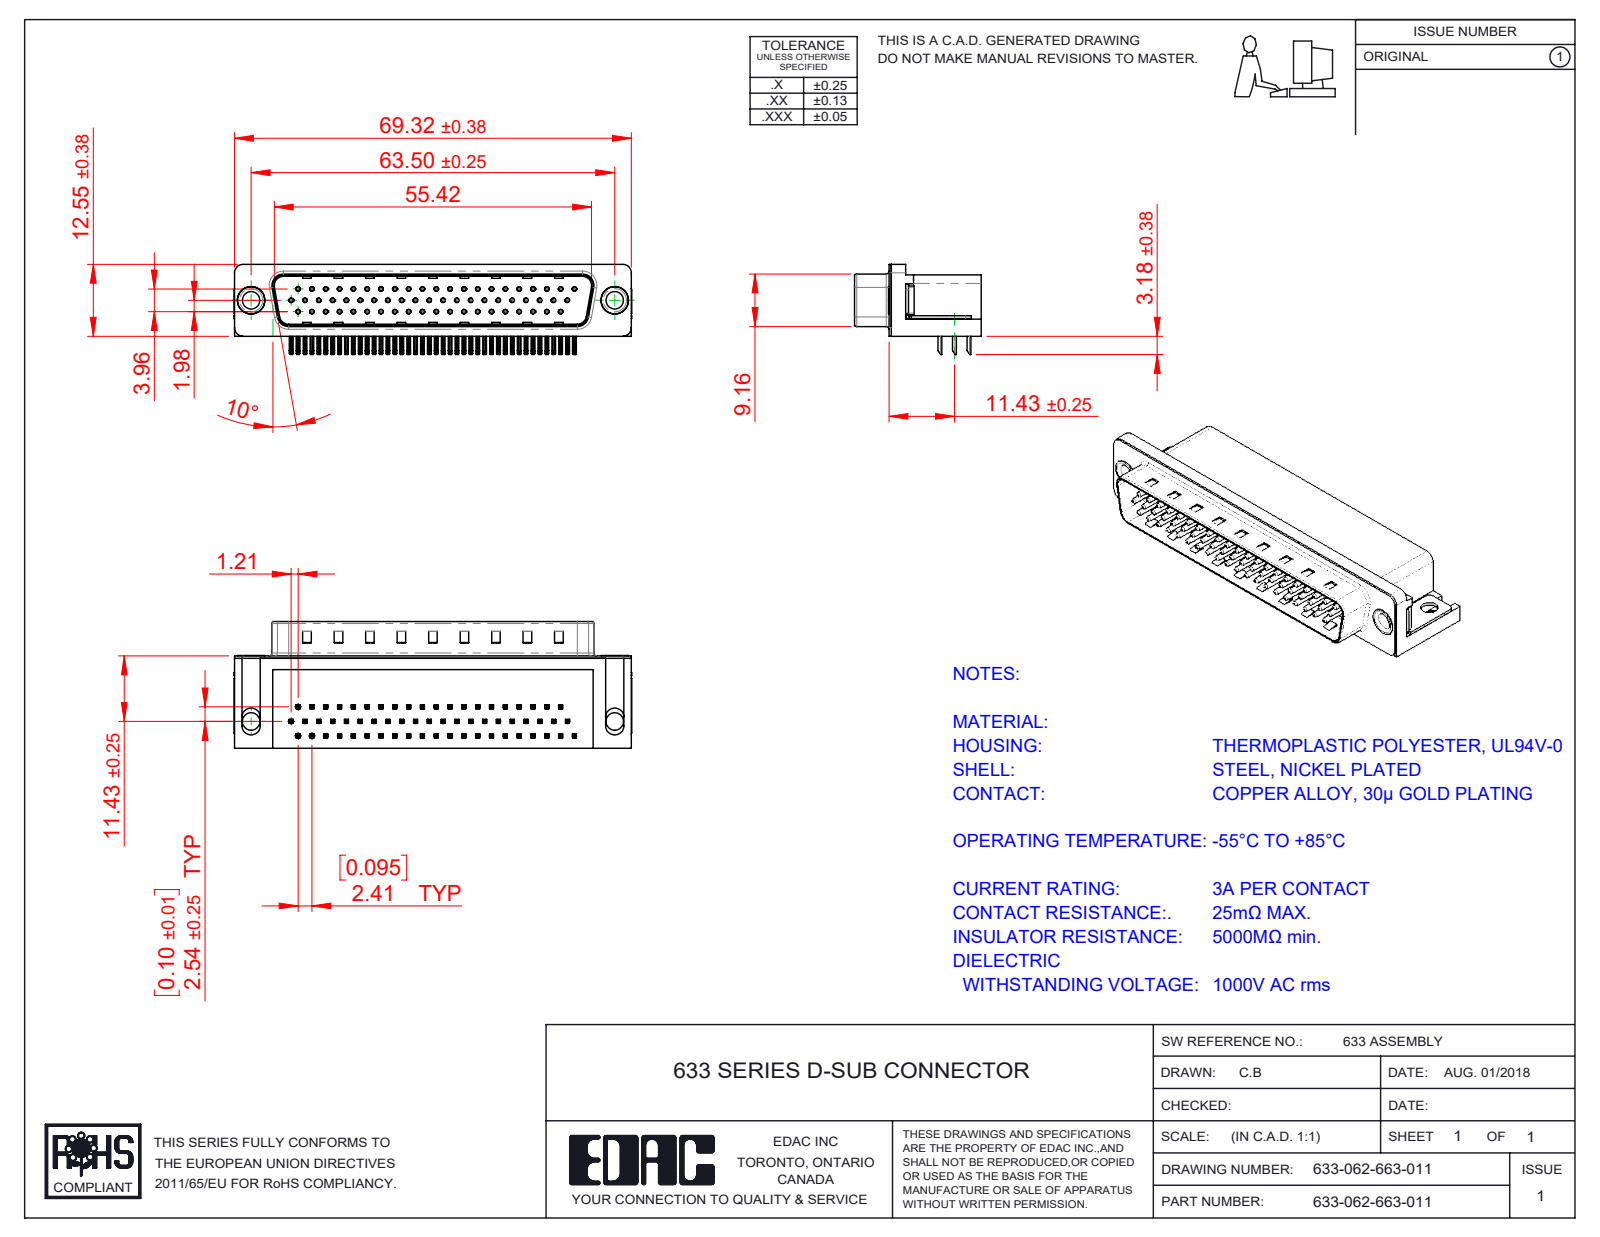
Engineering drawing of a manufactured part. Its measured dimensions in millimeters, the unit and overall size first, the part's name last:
Units: millimetres
Overall size (bounding box): 69.4 × 22.1 × 15.73
Round holes (diameter × count): ⌀0.35 ×62, ⌀0.8 ×62, ⌀3.05 ×4, ⌀4 ×2, ⌀4.8 ×2, ⌀5 ×2
Round bosses / shafts (diameter × count): ⌀0.75 ×62, ⌀4.9 ×2, ⌀4.75 ×2, ⌀3.85 ×2
Partial cylindrical surfaces — rounded edges, fillets, slot ends (radius × count): R0.25 ×256, R0.12 ×124, R1 ×16, R0.5 ×9, R1.6 ×8, R1.5 ×7, R0.9 ×4, R2 ×4
Main face-to-face distances: 0.4, 10.35, 15.7, 8.76, 2.9, 2.5, 2.54, 8.36, 2.1, 10.46
Hole centre spacings: 2.41, 4.82, 7.24, 9.65, 14.48, 16.89, 4.83, 7.23
Volume: 11 042 mm³ · Surface area: 13 374 mm²
Bodies: 68 solids, 5034 faces (3211 planar, 1424 cylindrical, 399 other)
Part name (STEP PRODUCT): 633 Contact Middle; 633 Contact Bottom; 633 Contact Top; 633 Thru Hole Rivet (+4 more)
STEP written by: SolidWorks 2016 (CONFIG_CONTROL_DESIGN)
